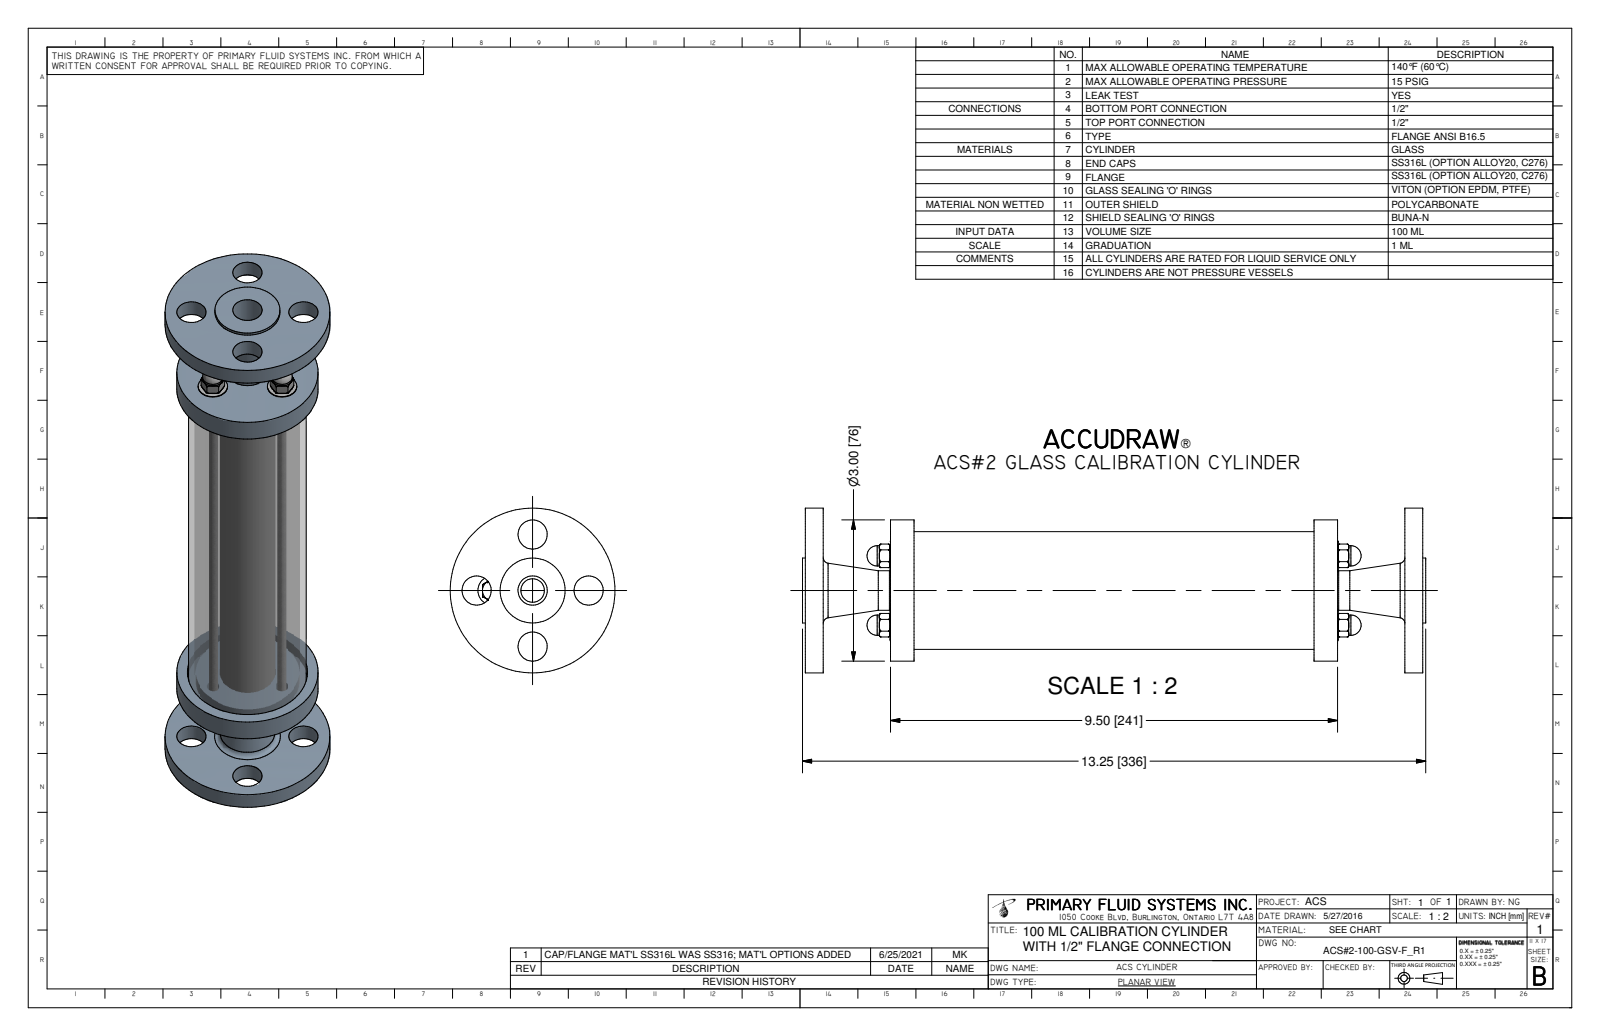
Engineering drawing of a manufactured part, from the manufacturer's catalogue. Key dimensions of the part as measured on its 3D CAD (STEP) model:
Part name (STEP PRODUCT): ACS#2-100-GSV-F_R0; ACS-3-100-METAL-S_R1; ACS-2-100-PC_R6; ACS-1-100-A_R0 (+4 more)
STEP written by: Autodesk Inventor 2009 (AUTOMOTIVE_DESIGN)
Units: inches
Bodies: 21 solids, 455 faces (46 planar, 57 cylindrical, 352 other)
Overall size (bounding box): 13.245 × 3.5 × 3.5
Volume: 24.51 in³ · Surface area: 342.4 in²
Round holes (diameter × count): ⌀0.62 ×4, ⌀0.18 ×3, ⌀0.266 ×3, ⌀0.281 ×3, ⌀0.622 ×1, ⌀1.071 ×1, ⌀1.2 ×1, ⌀2.25 ×1, ⌀2.55 ×1
Round bosses / shafts (diameter × count): ⌀0.625 ×3, ⌀0.187 ×3, ⌀3.5 ×1, ⌀3 ×1, ⌀2.5 ×1, ⌀2.2 ×1, ⌀1.38 ×1, ⌀1.181 ×1
Main face-to-face distances: 1.81, 11.31, 0.38, 12.74, 1.43, 10.93, 2.31, 10.81, 1.93, 10.43
Hole centre spacings: 0.85, 1.19, 1.683, 1.062, 1.472, 1.973, 0.622, 1.463
